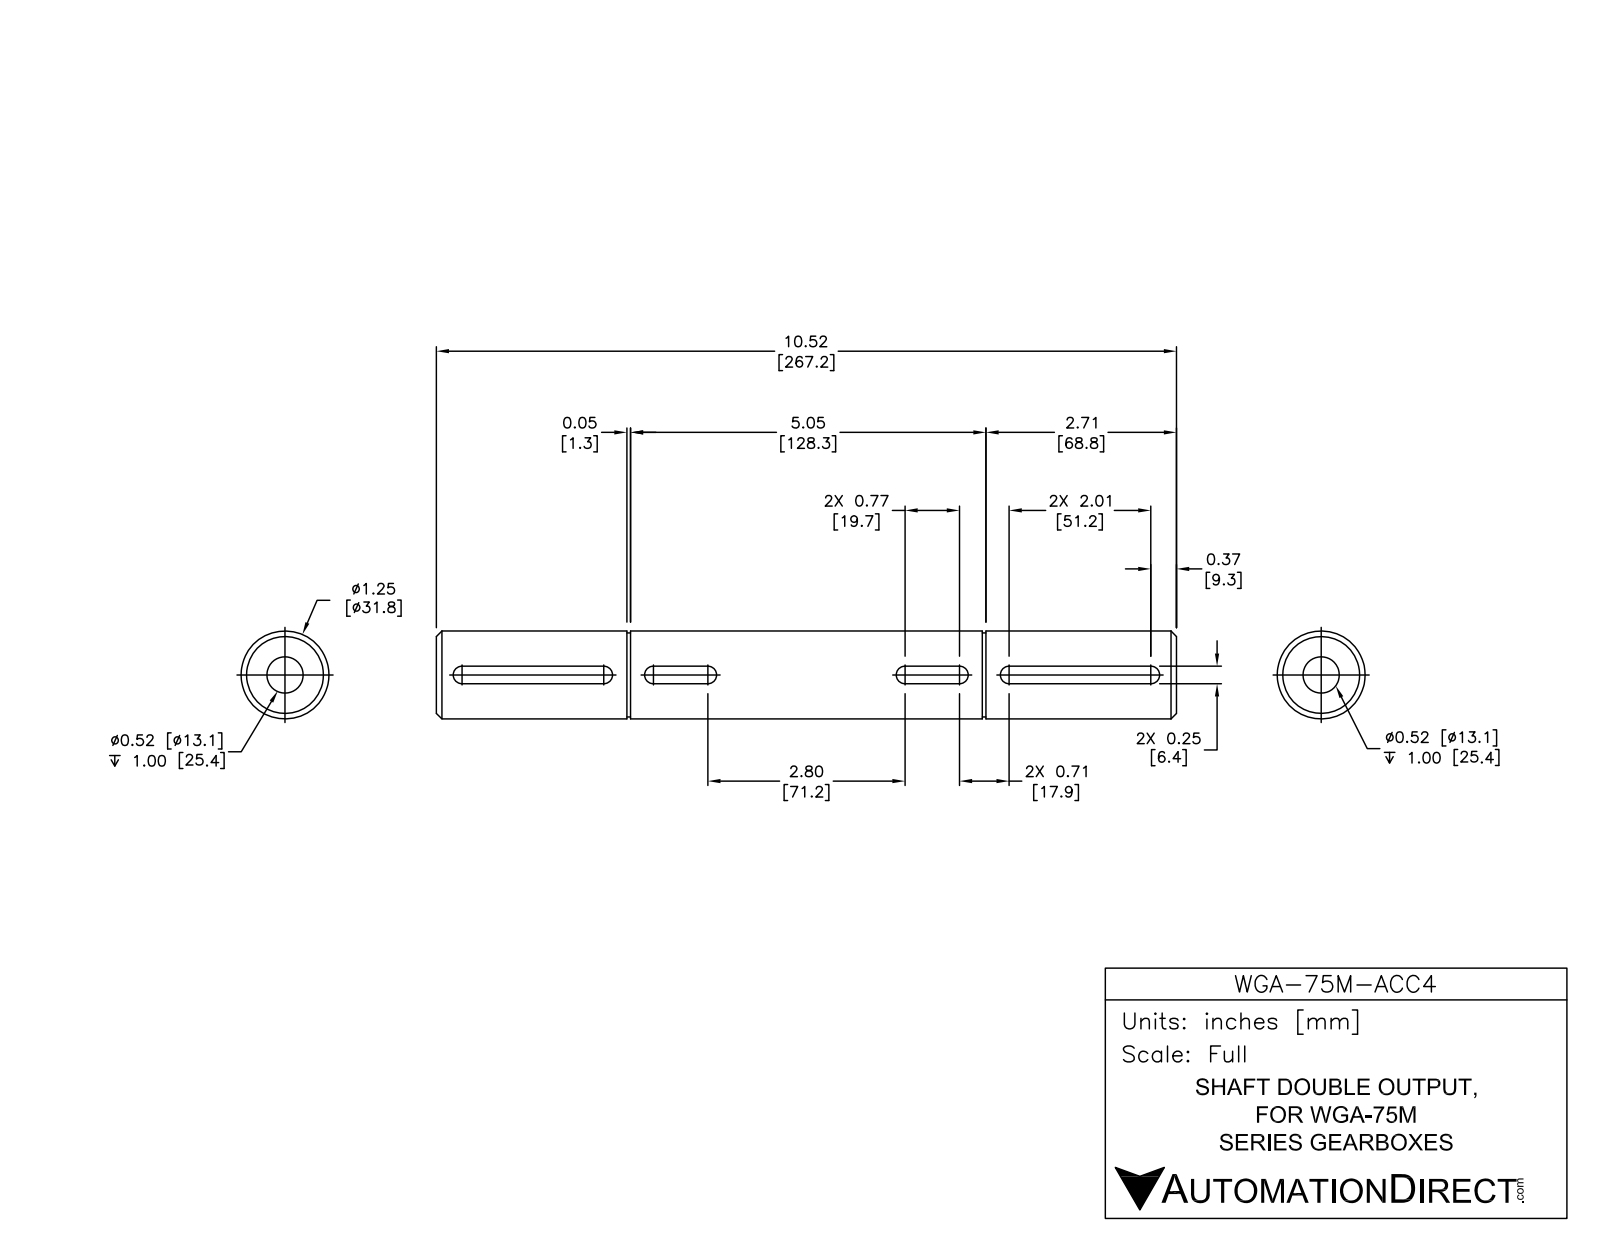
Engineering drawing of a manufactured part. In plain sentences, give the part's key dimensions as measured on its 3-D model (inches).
The part is named "WGA-75M-ACC4". Its 3-D file was written by "SolidWorks 2014 (AUTOMOTIVE_DESIGN)". It is 1 solid with 48 faces: 18 planar, 22 cylindrical and 8 other. Overall it measures 10.52 by 1.25 by 1.25 inches. Its volume is 12.23 cubic inches and its surface area 48.87 square inches. Round holes: 1 of diameter 0.516. Round bosses or shafts: 1 of diameter 1.25, 1 of diameter 1.193. Partial cylindrical surfaces (rounded edges, fillets, slot ends): 8 of radius 0.125. The main face-to-face distances are 10.52, 0.25, 0.25, 2.76, 7.76, 2.709, 7.811, 5.051, 0.051, 0.25.
